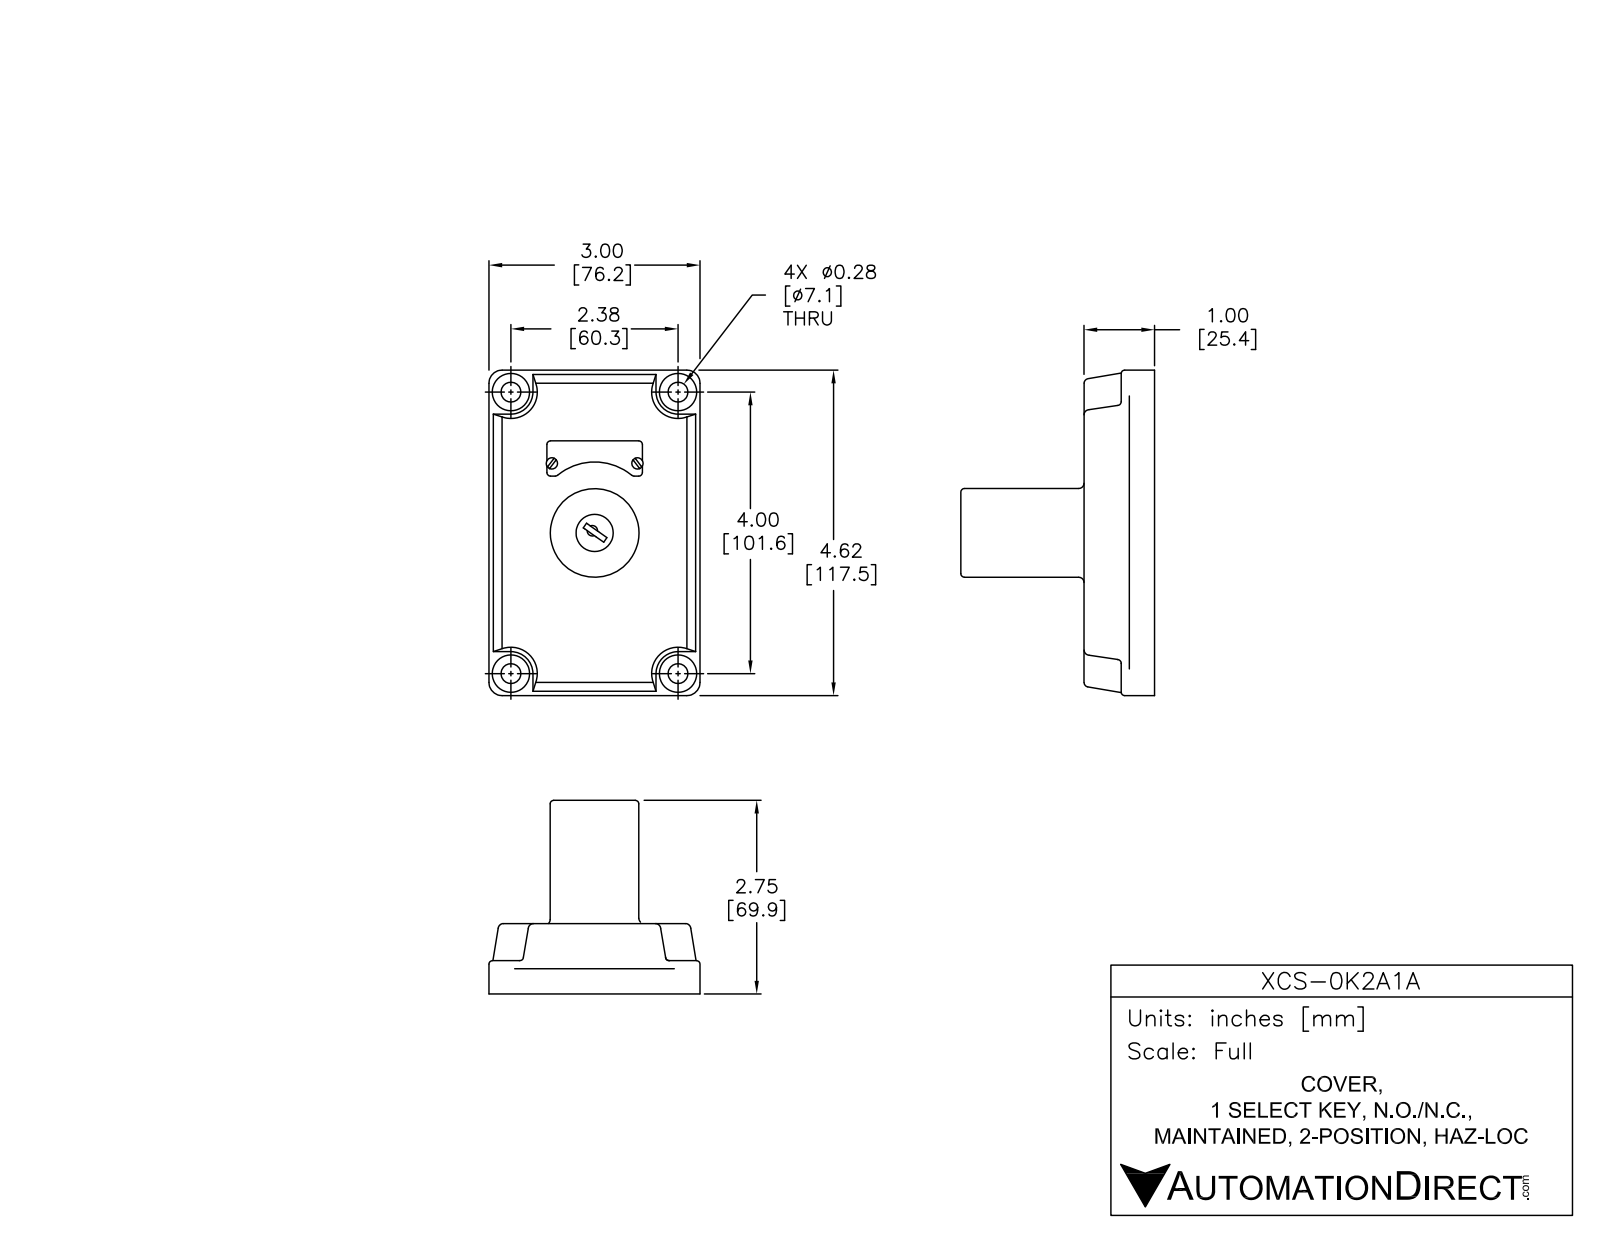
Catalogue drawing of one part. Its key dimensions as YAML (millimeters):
part_name: "XCS-0K2A1A"
step_written_by: "SolidWorks 2015 (AUTOMOTIVE_DESIGN)"
units: millimeters
bodies: {solids: 14, faces: 549, planar: 228, cylindrical: 186, other: 135}
overall_size: [139.37, 119.33, 78.74]
volume: 234905
surface_area: 64266
round_holes:
  - {diameter: 6.86, count: 4}
  - {diameter: 4.99, count: 2}
  - {diameter: 13.5, count: 1}
  - {diameter: 14.5, count: 1}
round_bosses_or_shafts:
  - {diameter: 3.3, count: 8}
  - {diameter: 11.6, count: 4}
  - {diameter: 6.35, count: 4}
  - {diameter: 31.9, count: 1}
  - {diameter: 24, count: 1}
partial_cylinders:
  - {radius: 0.25, count: 28}
  - {radius: 1.27, count: 10}
  - {radius: 0.51, count: 8}
  - {radius: 1.4, count: 8}
  - {radius: 2, count: 8}
  - {radius: 2.54, count: 4}
  - {radius: 3.5, count: 4}
  - {radius: 9.65, count: 4}
face_to_face_distances: [13.34, 12.7, 26.04, 0.63, 0.9, 38.13, 50.83, 64.17, 37.23, 49.93]
hole_center_spacings: [59.11, 60.46, 101.6, 118.23, 17.33]
